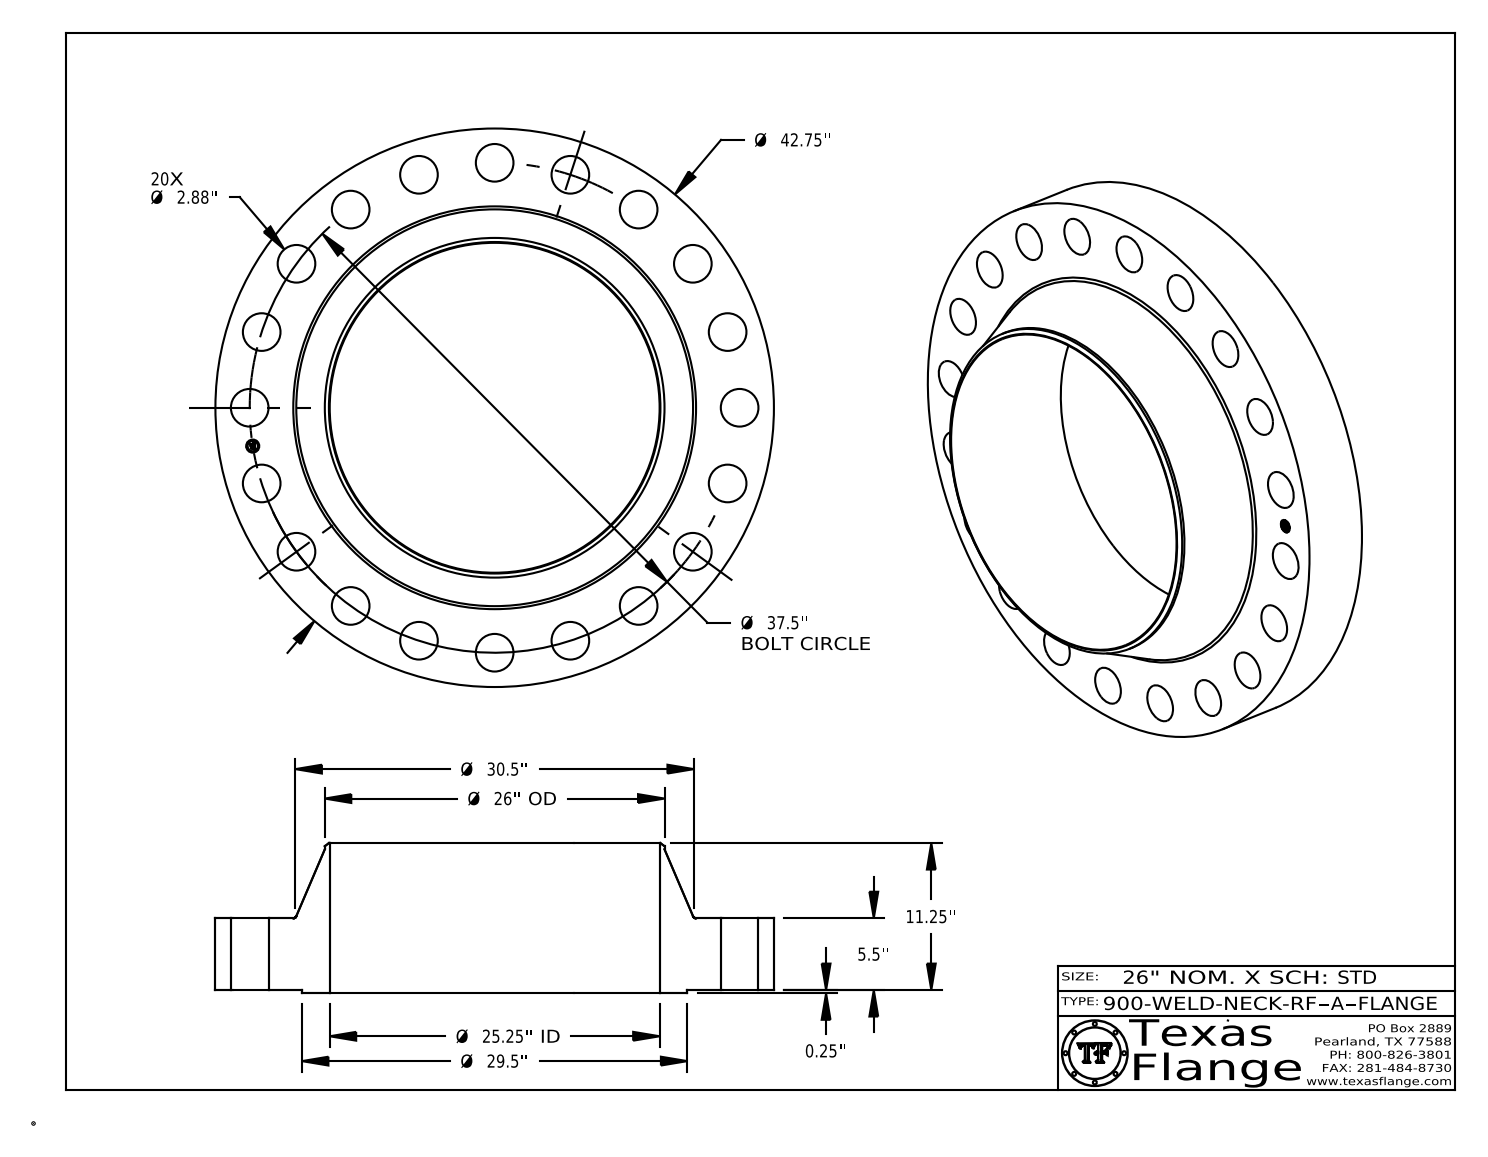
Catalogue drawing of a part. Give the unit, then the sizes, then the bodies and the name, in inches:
Units: inches
Overall size (bounding box): 42.75 × 42.75 × 11.5
Round holes (diameter × count): ⌀2.88 ×20, ⌀1 ×1, ⌀25.25 ×1
Round bosses / shafts (diameter × count): ⌀0.061 ×8, ⌀42.75 ×1, ⌀29.5 ×1, ⌀26 ×1, ⌀0.788 ×1
Main face-to-face distances: 5.5, 5.75, 0.25, 11.5, 11.25, 0.015, 5.735, 5.485, 5.765, 0.298
Hole centre spacings: 5.866, 11.588, 17.024, 22.042, 33.413, 35.665, 37.038, 18.75
Volume: 5 153 in³ · Surface area: 4 610 in²
Bodies: 1 solid, 443 faces (369 planar, 68 cylindrical, 6 other)
Part name (STEP PRODUCT): 900-WELD-NECK-RF, Series A
STEP written by: CATIA V5 STEP AP214 (AUTOMOTIVE_DESIGN)
